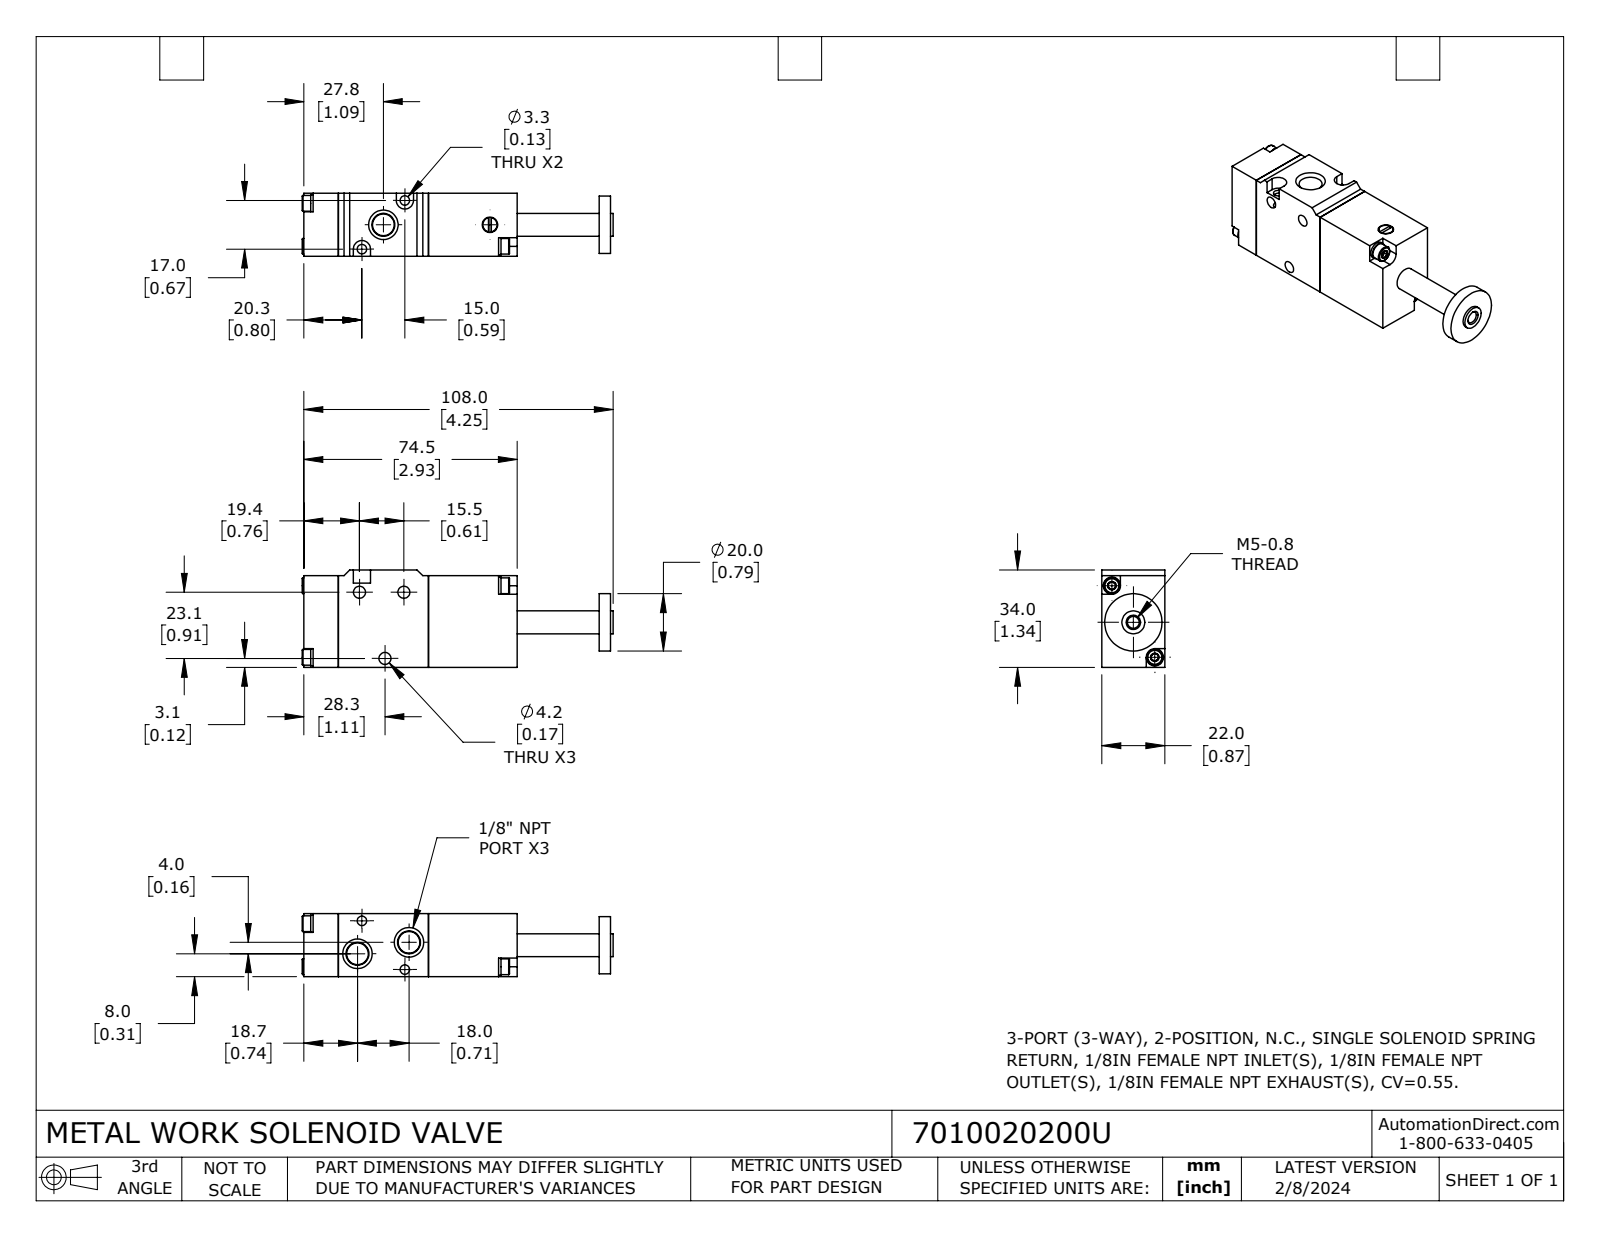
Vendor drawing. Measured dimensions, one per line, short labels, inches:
name: 7010020200U
written by: SolidWorks 2023 (CONFIG_CONTROL_DESIGN)
unit: in
bodies: 11 solids, 254 faces (120 planar, 64 cylindrical, 70 other)
size: 4.276 × 1.339 × 0.866
volume: 3.251 in³; area: 26.36 in²
holes: 4× ⌀0.118, 3× ⌀0.165, 2× ⌀0.13, 1× ⌀0.163, 1× ⌀0.213
bosses: 4× ⌀0.236, 4× ⌀0.217, 1× ⌀0.787, 1× ⌀0.315, 1× ⌀0.197
rounds: 2× R0.118
face distances: 0.866, 1.24, 1.26, 0.472, 1.713, 1.22, 2.933, 2.461, 1.339, 0.079
hole spacings: 0.564, 0.584, 0.591, 0.984, 1.148, 0.61, 0.893, 0.946
